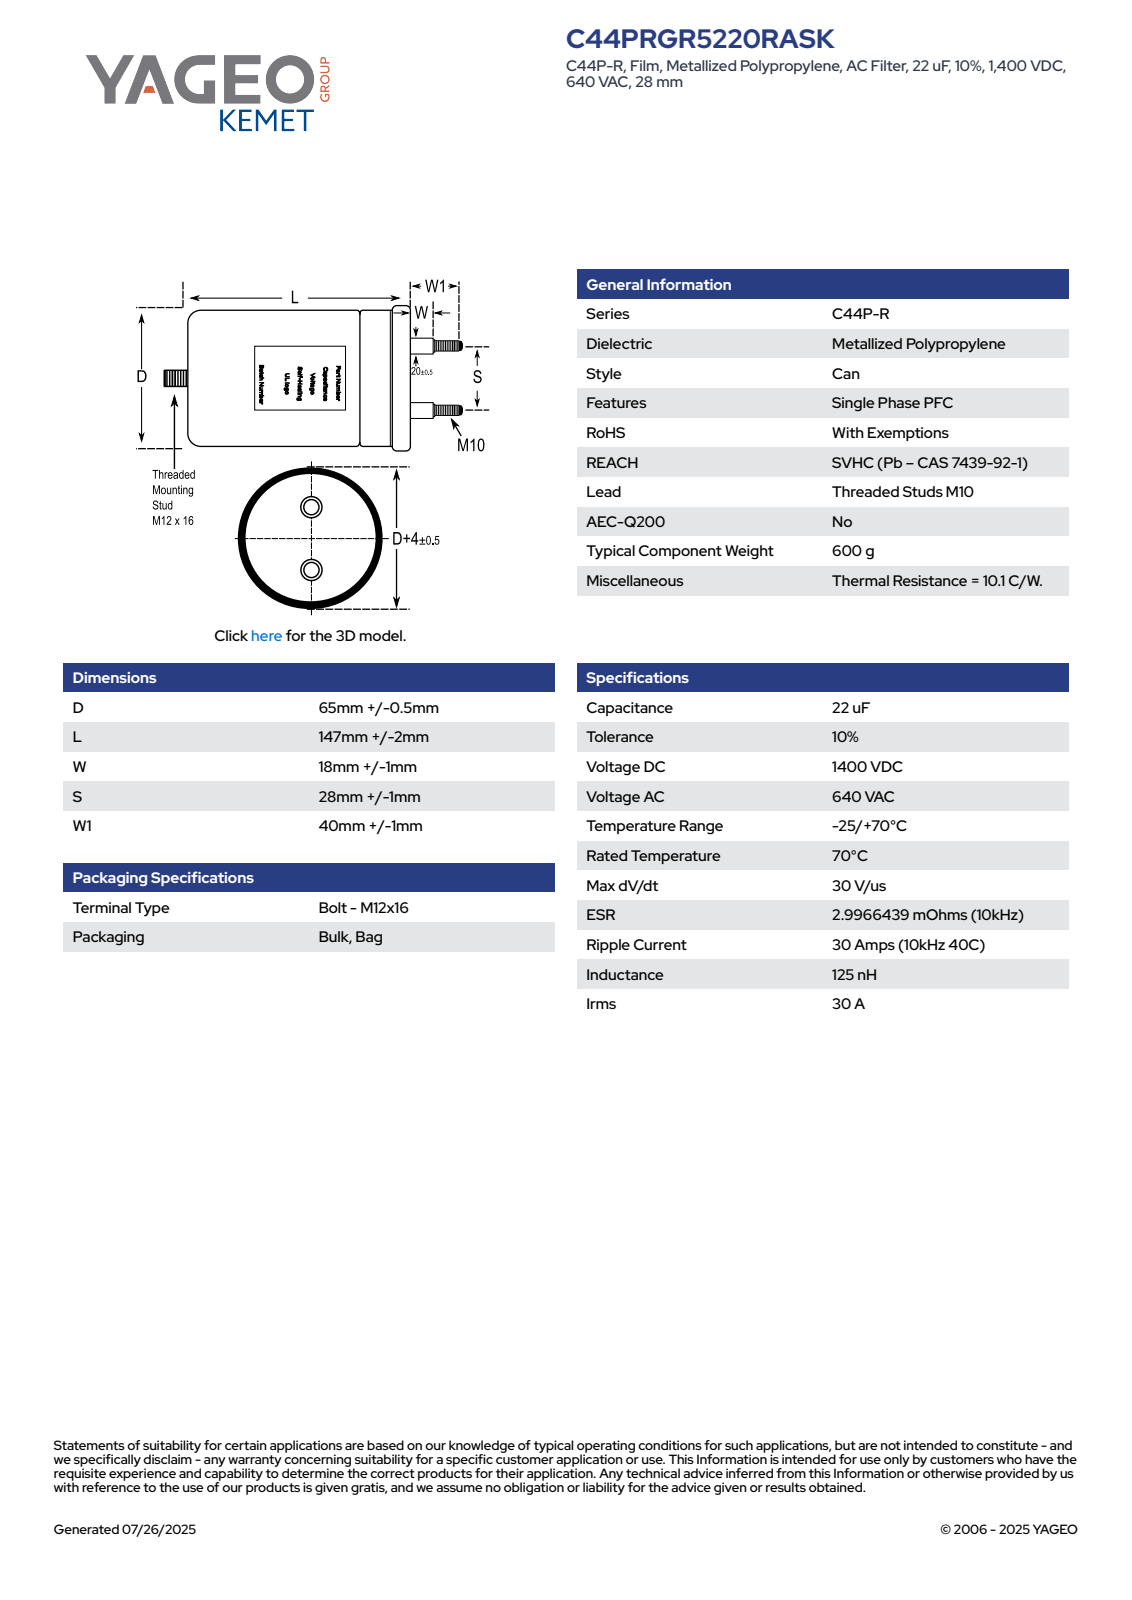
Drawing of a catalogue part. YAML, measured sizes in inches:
part_name: "CFP_C44P_65X147_D65.5L149S28"
step_written_by: "SolidWorks 2014 (AUTOMOTIVE_DESIGN)"
units: inches
bodies: {solids: 1, faces: 105, planar: 32, cylindrical: 36, other: 37}
overall_size: [8.11, 2.756, 2.756]
volume: 31.77
surface_area: 65.36
round_bosses_or_shafts:
  - {diameter: 0.472, count: 3}
  - {diameter: 0.807, count: 2}
  - {diameter: 0.394, count: 2}
  - {diameter: 2.756, count: 1}
  - {diameter: 2.579, count: 1}
partial_cylinders:
  - {radius: 1.29, count: 1}
face_to_face_distances: [5.866, 6.575, 0.709, 5.678, 0.188, 0.897, 7.48, 1.802, 1.614, 0.906]
